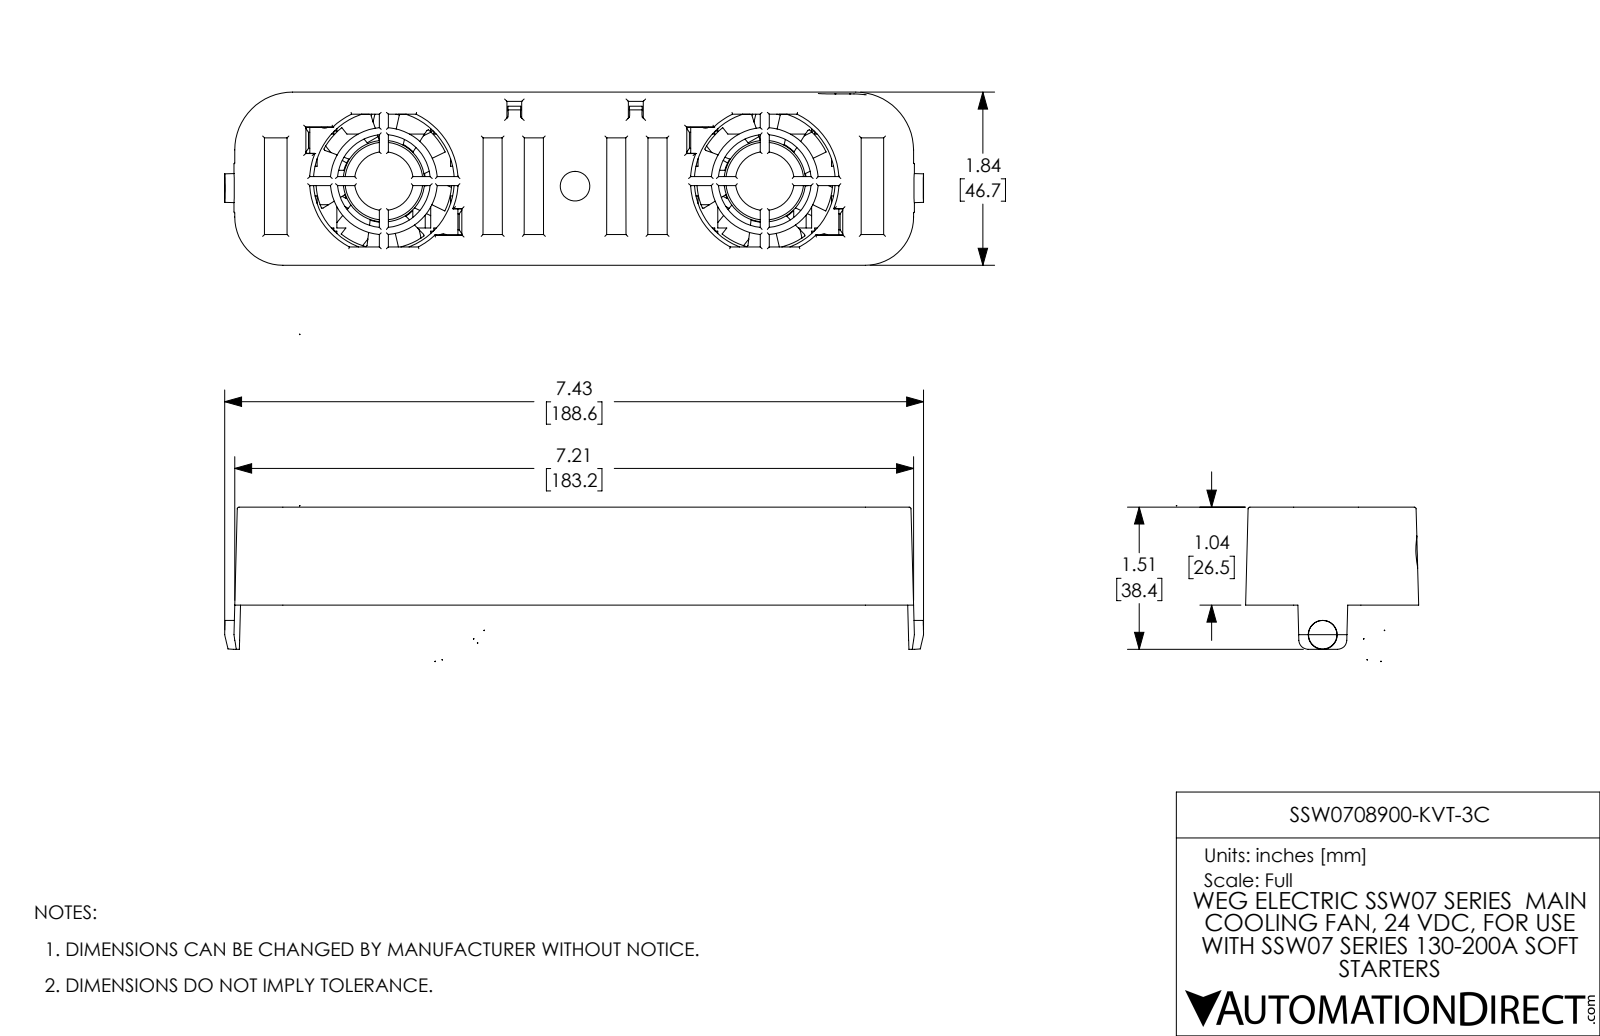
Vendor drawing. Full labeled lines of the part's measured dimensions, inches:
Part name (STEP PRODUCT): SSW0708900-KVT-3C
STEP written by: SolidWorks 2017 (AUTOMOTIVE_DESIGN)
Units: inches
Bodies: 11 solids, 1046 faces (638 planar, 256 cylindrical, 152 other)
Overall size (bounding box): 7.426 × 2.574 × 1.657
Volume: 3.222 in³ · Surface area: 102.3 in²
Round holes (diameter × count): ⌀0.138 ×8, ⌀0.814 ×2, ⌀1.496 ×2, ⌀0.315 ×1
Round bosses / shafts (diameter × count): ⌀0.871 ×2, ⌀0.866 ×2
Partial cylindrical surfaces — rounded edges, fillets, slot ends (radius × count): R0.02 ×42, R0.079 ×9, R1.217 ×8, R0.098 ×2, R0.157 ×2, R0.44 ×2, R0.551 ×2, R0.614 ×2
Main face-to-face distances: 0.062, 0.087, 0.074, 0.131, 0.791, 0.878, 0.326, 0.628, 1.575, 0.274
Hole centre spacings: 0.891, 1.26, 4.047, 1.781, 3.475, 4.239, 4.719, 2.787
